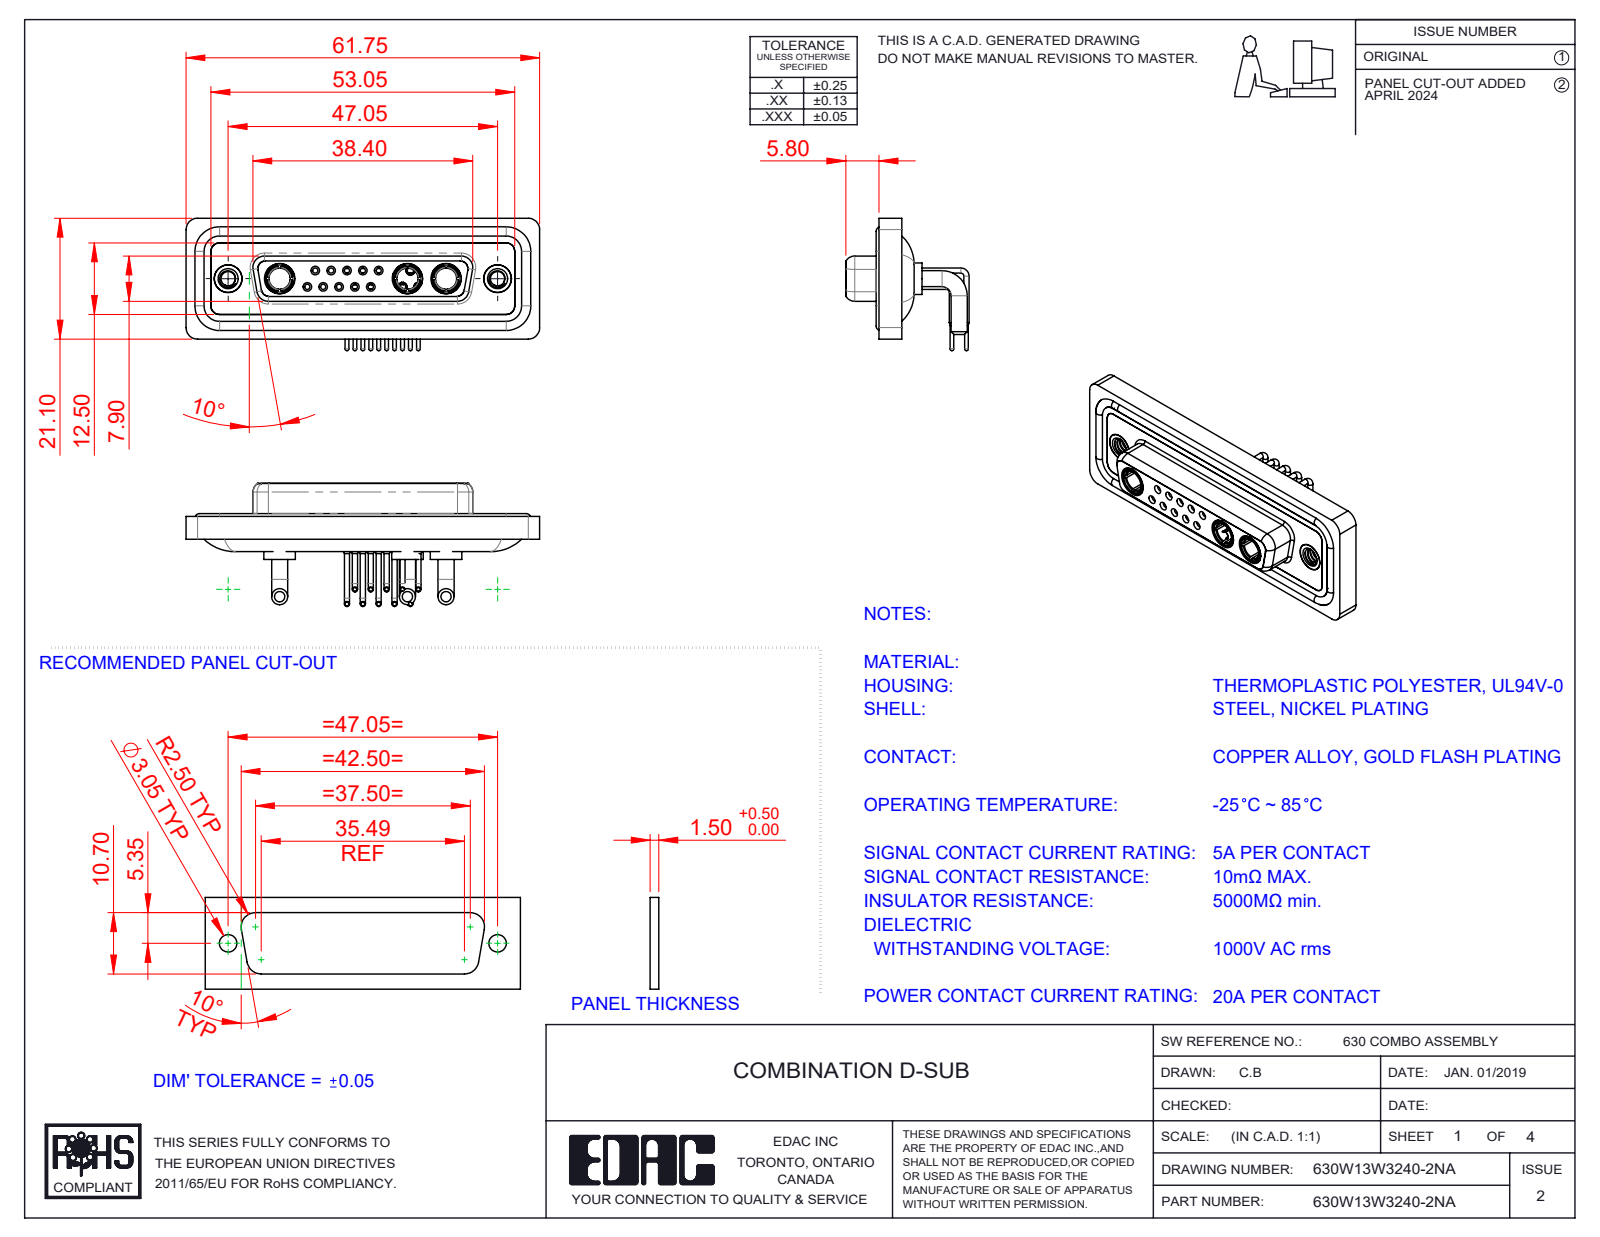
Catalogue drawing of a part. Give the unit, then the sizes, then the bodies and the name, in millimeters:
Units: millimetres
Overall size (bounding box): 61.75 × 23.12 × 21.53
Round holes (diameter × count): ⌀0.9 ×10, ⌀1.1 ×10, ⌀1.5 ×10, ⌀2 ×10, ⌀1.6 ×5, ⌀1.7 ×5, ⌀4.85 ×5, ⌀3.7 ×3, ⌀5.3 ×3, ⌀2.5 ×2, ⌀4 ×2, ⌀4.05 ×2
Round bosses / shafts (diameter × count): ⌀0.9 ×15, ⌀1.6 ×12, ⌀0.65 ×10, ⌀2.8 ×6, ⌀2 ×5, ⌀1.5 ×5, ⌀5.5 ×3, ⌀5.2 ×3
Partial cylindrical surfaces — rounded edges, fillets, slot ends (radius × count): R1.5 ×18, R2 ×18, R1.35 ×8, R1.6 ×8, R0.25 ×4, R0.5 ×4, R0.6 ×4, R0.65 ×4
Main face-to-face distances: 0.4, 1.8, 4.1, 1.1, 1.6, 1.5, 3.1, 2.5, 3.7, 1.4
Hole centre spacings: 3.16, 2.77, 5.54, 5.04, 8.31, 5.03, 7.49, 11.08
Volume: 8 463 mm³ · Surface area: 14 299 mm²
Bodies: 23 solids, 1144 faces (342 planar, 491 cylindrical, 311 other)
Part name (STEP PRODUCT): 630Combo Housing_13W3; 630Combo Waterproof Housing_25 Contacts; 630Combo Contact Row 1_50 Contacts; 630Combo Contact Row 2_50 Contacts (+5 more)
STEP written by: SolidWorks 2023 (CONFIG_CONTROL_DESIGN)
